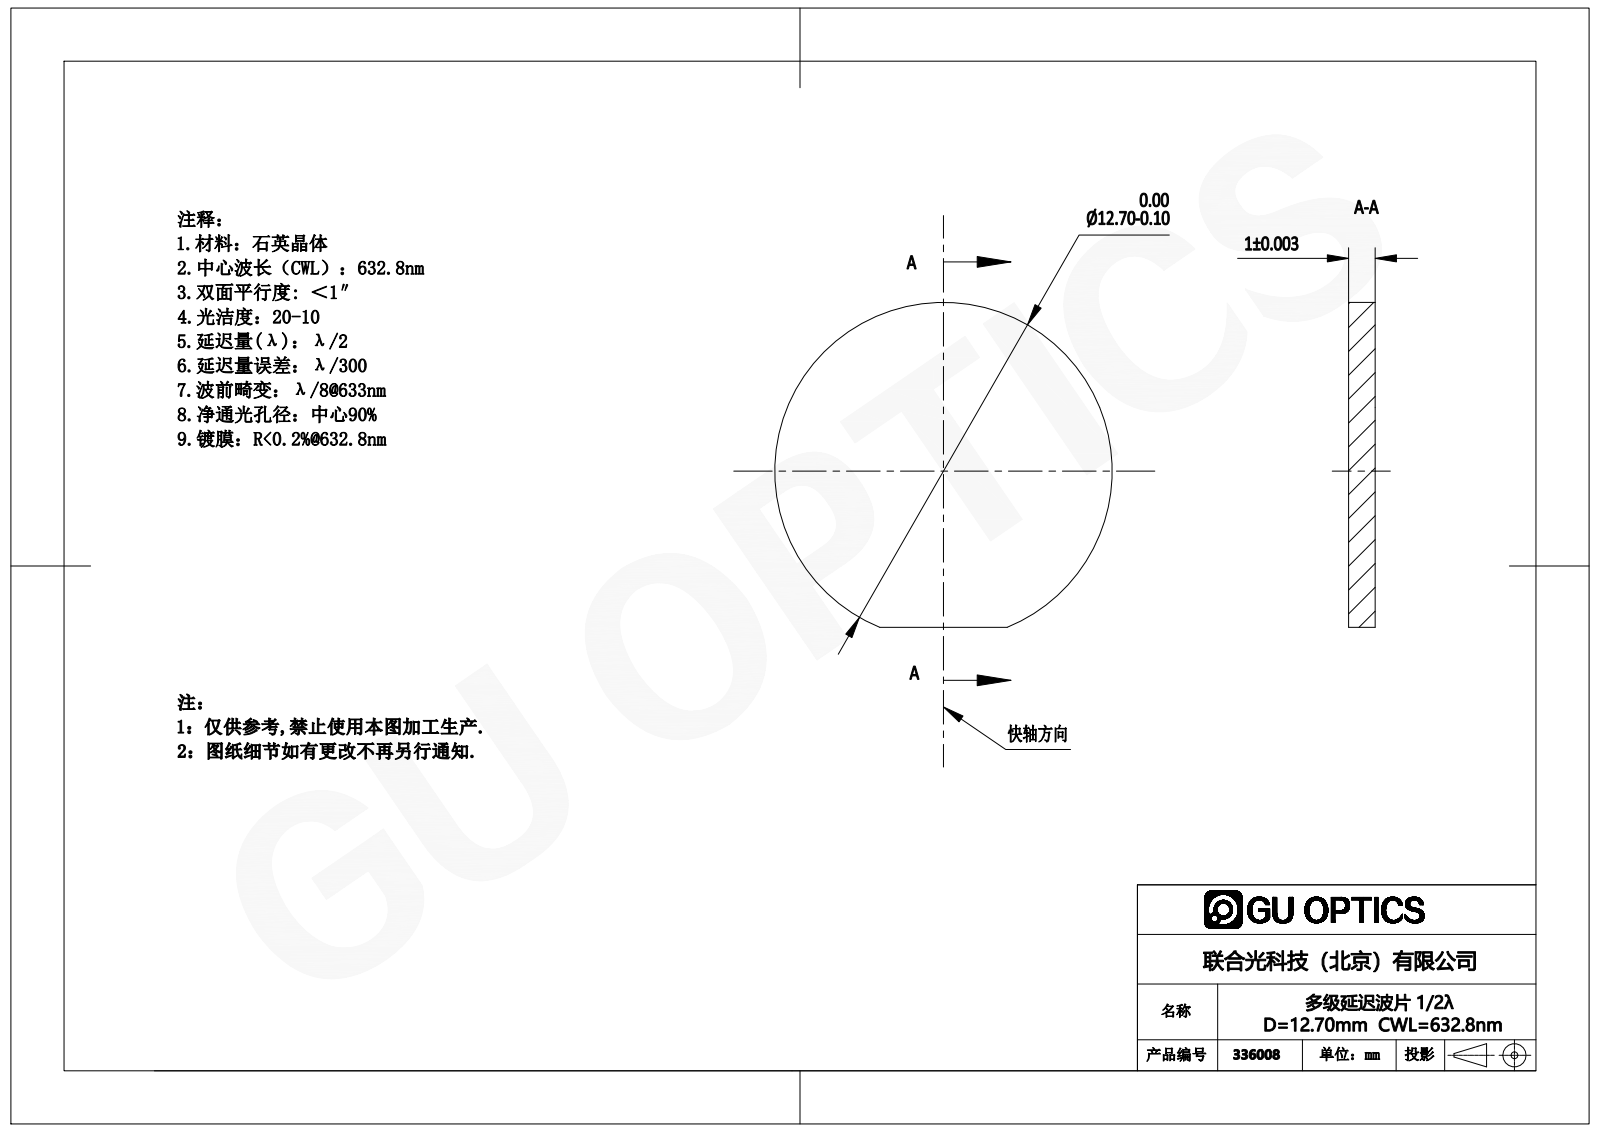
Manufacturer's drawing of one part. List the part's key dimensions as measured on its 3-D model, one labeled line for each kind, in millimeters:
Part name (STEP PRODUCT): 336000
STEP written by: SolidWorks 2019 (AUTOMOTIVE_DESIGN)
Units: millimetres
Bodies: 1 solid, 6 faces (3 planar, 3 cylindrical, 0 other)
Overall size (bounding box): 12.7 × 12.23 × 1
Volume: 125 mm³ · Surface area: 290 mm²
Round bosses / shafts (diameter × count): ⌀12.7 ×1
Main face-to-face distances: 1
